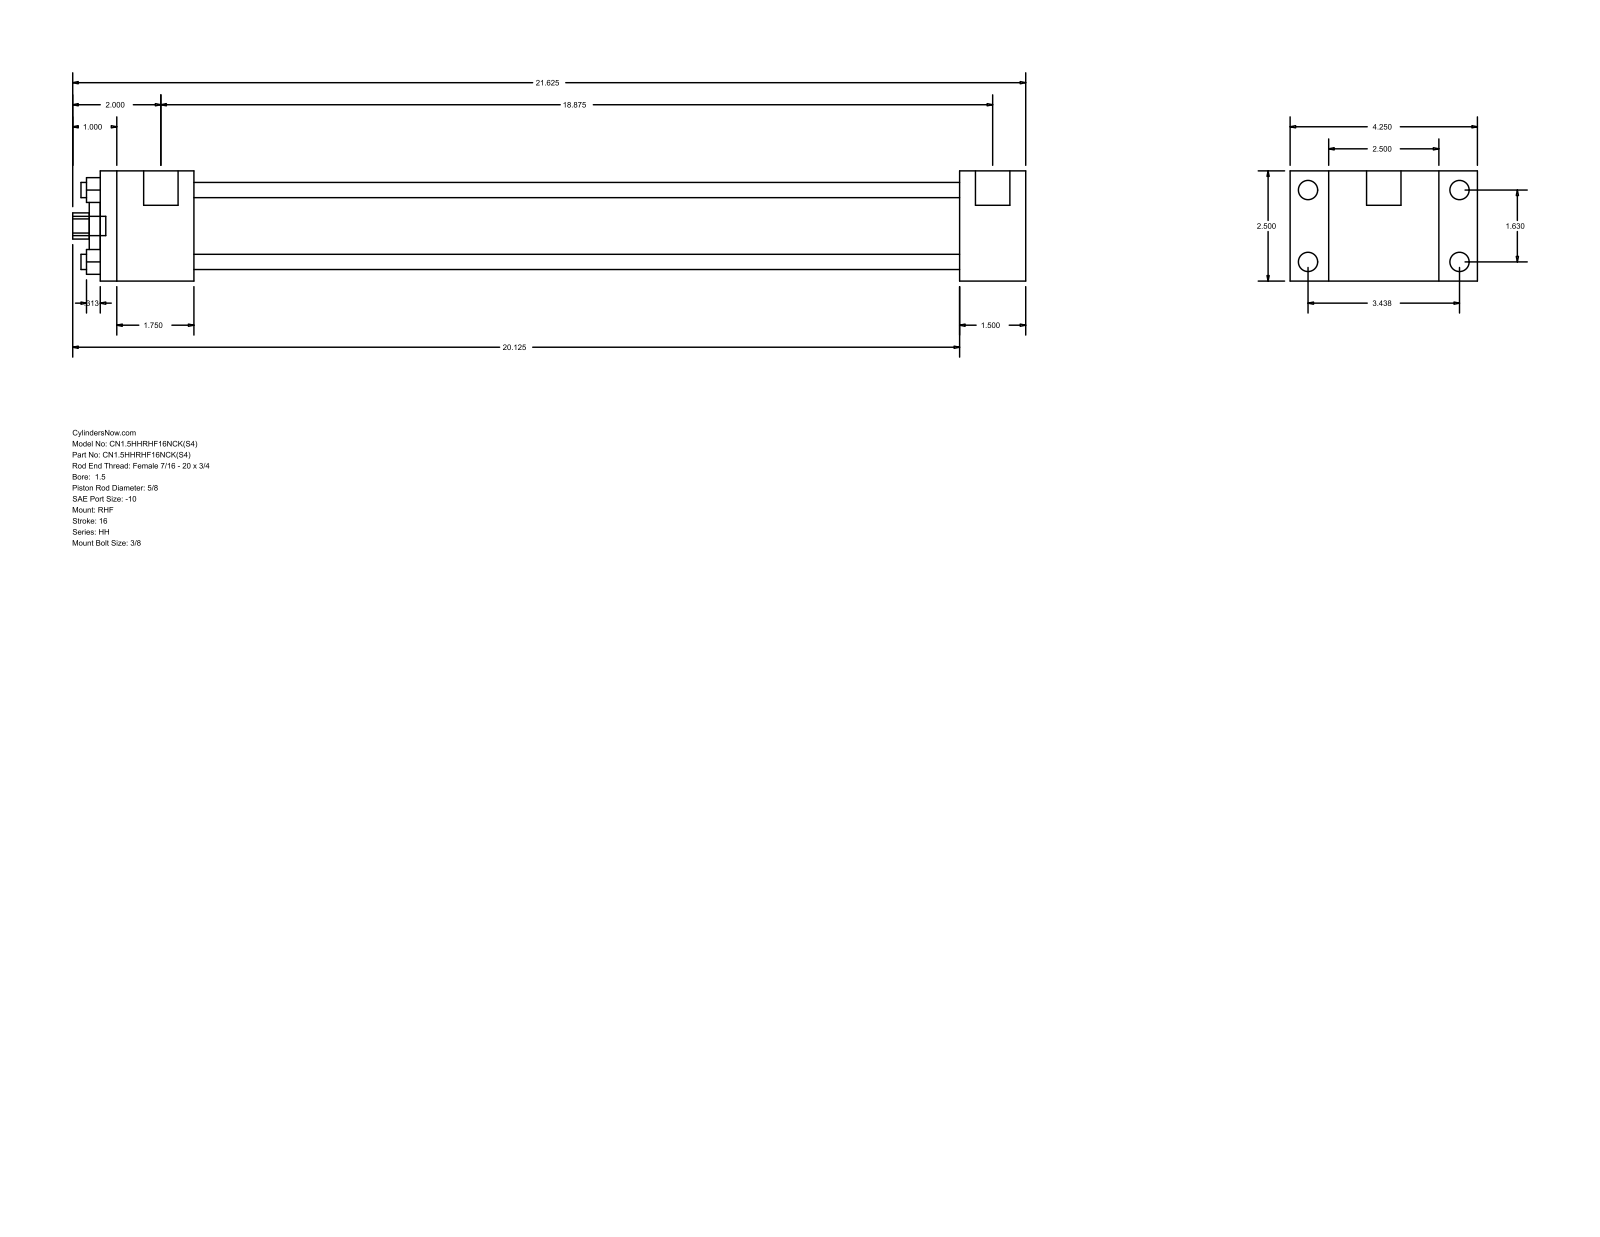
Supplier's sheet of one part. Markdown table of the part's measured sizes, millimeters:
| quantity | value |
| --- | --- |
| part name | HH_RHF__0150_0.625 |
| STEP written by | GSSL Pune (CONFIG_CONTROL_DESIGN) |
| units | millimeters |
| bodies | 0 solids, 88 faces (60 planar, 28 cylindrical, 0 other) |
| overall size | 549.27 × 107.95 × 63.5 |
| round holes (diameter × count) | 8.76 × 4, 15.88 × 1, 28.57 × 1, 44.45 × 1 |
| round bosses / shafts (diameter × count) | 11.13 × 4, 5.56 × 4, 19.84 × 2, 11.11 × 1 |
| partial cylindrical surfaces (radius × count) | 7.54 × 1 |
| main face-to-face distances | 63.5, 22.23, 85.73, 38.09, 495.3, 533.39, 107.96, 53.97, 441.33, 479.42 |
| hole center spacings | 29.27, 41.4, 58.55 |
